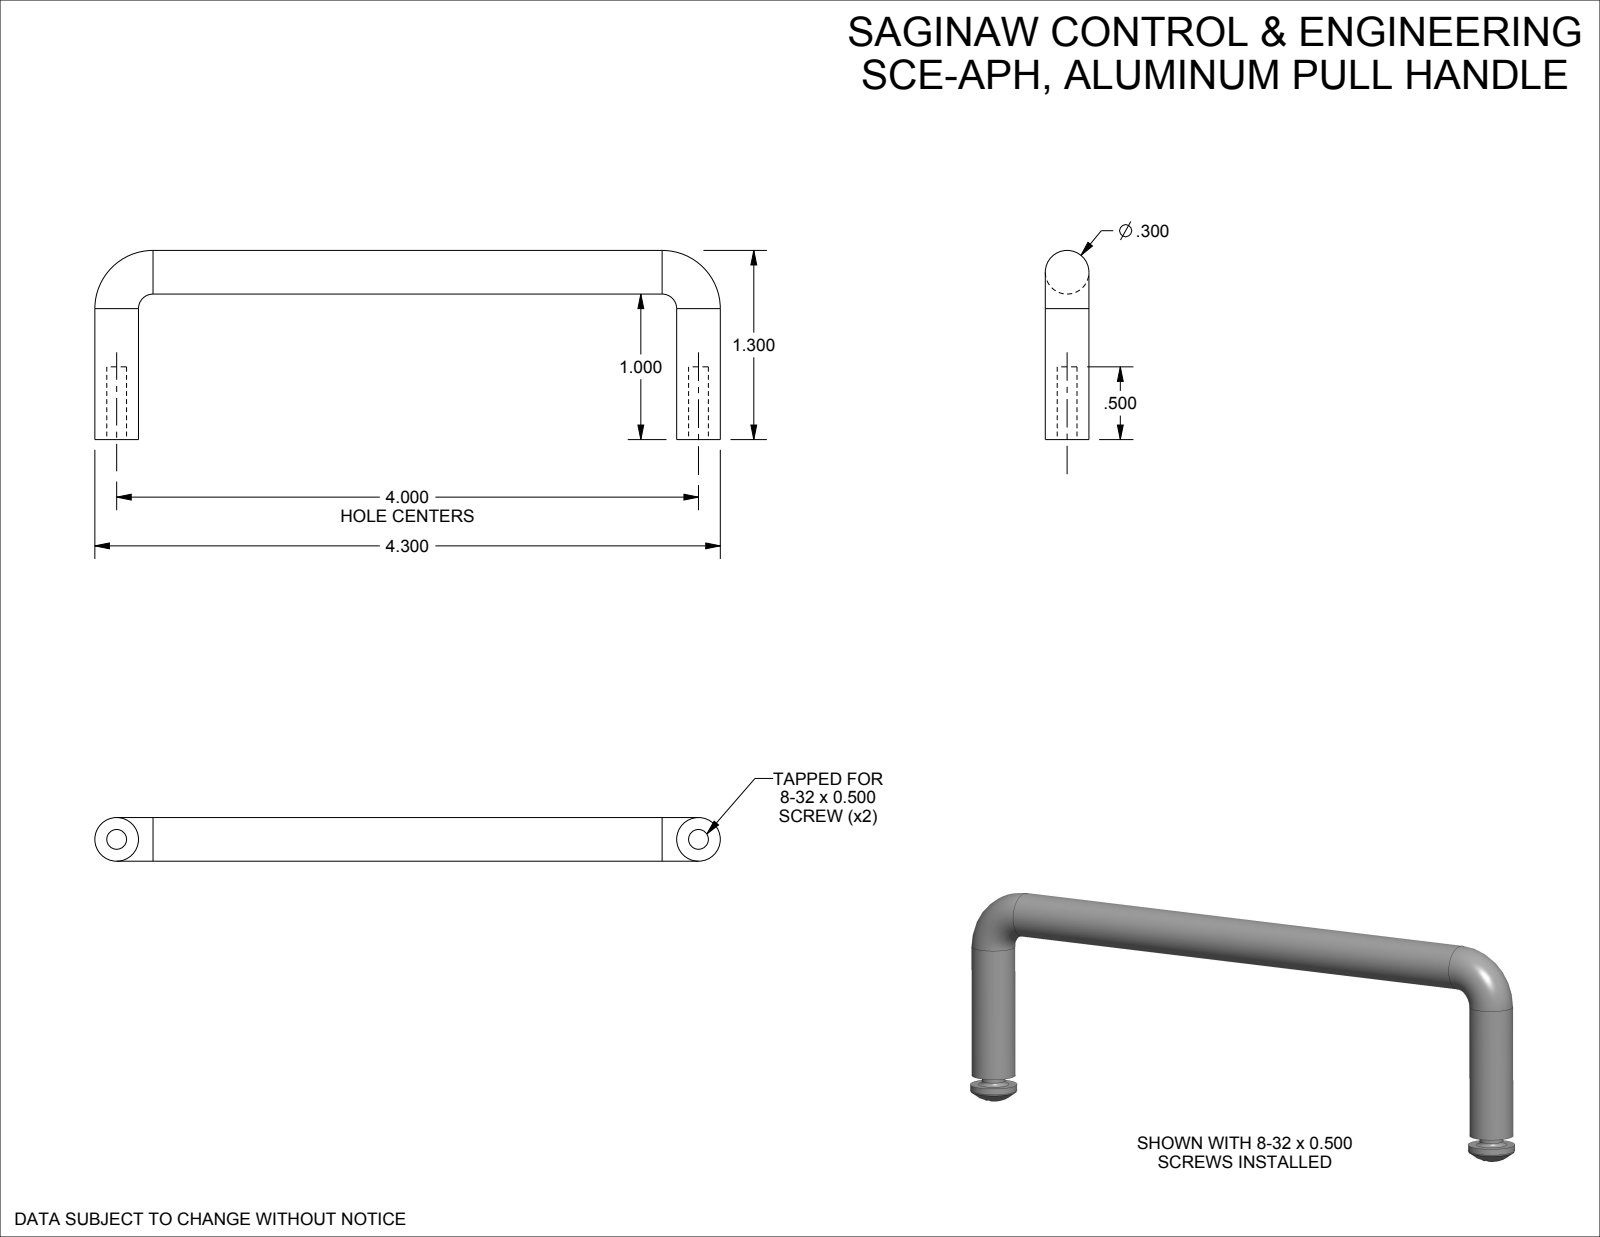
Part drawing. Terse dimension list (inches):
name: SCE-APH
written by: SolidWorks 2019 (AUTOMOTIVE_DESIGN)
unit: in
bodies: 3 solids, 99 faces (40 planar, 9 cylindrical, 50 other)
size: 4.322 × 1.473 × 0.322
volume: 0.448 in³; area: 7.308 in²
holes: 2× ⌀0.136
bosses: 3× ⌀0.3, 2× ⌀0.322, 2× ⌀0.162
face distances: 0.063, 0.5, 0.437, 0.563, 2, 0.087, 3.464, 0.087, 0.03, 2.087
hole spacings: 4
